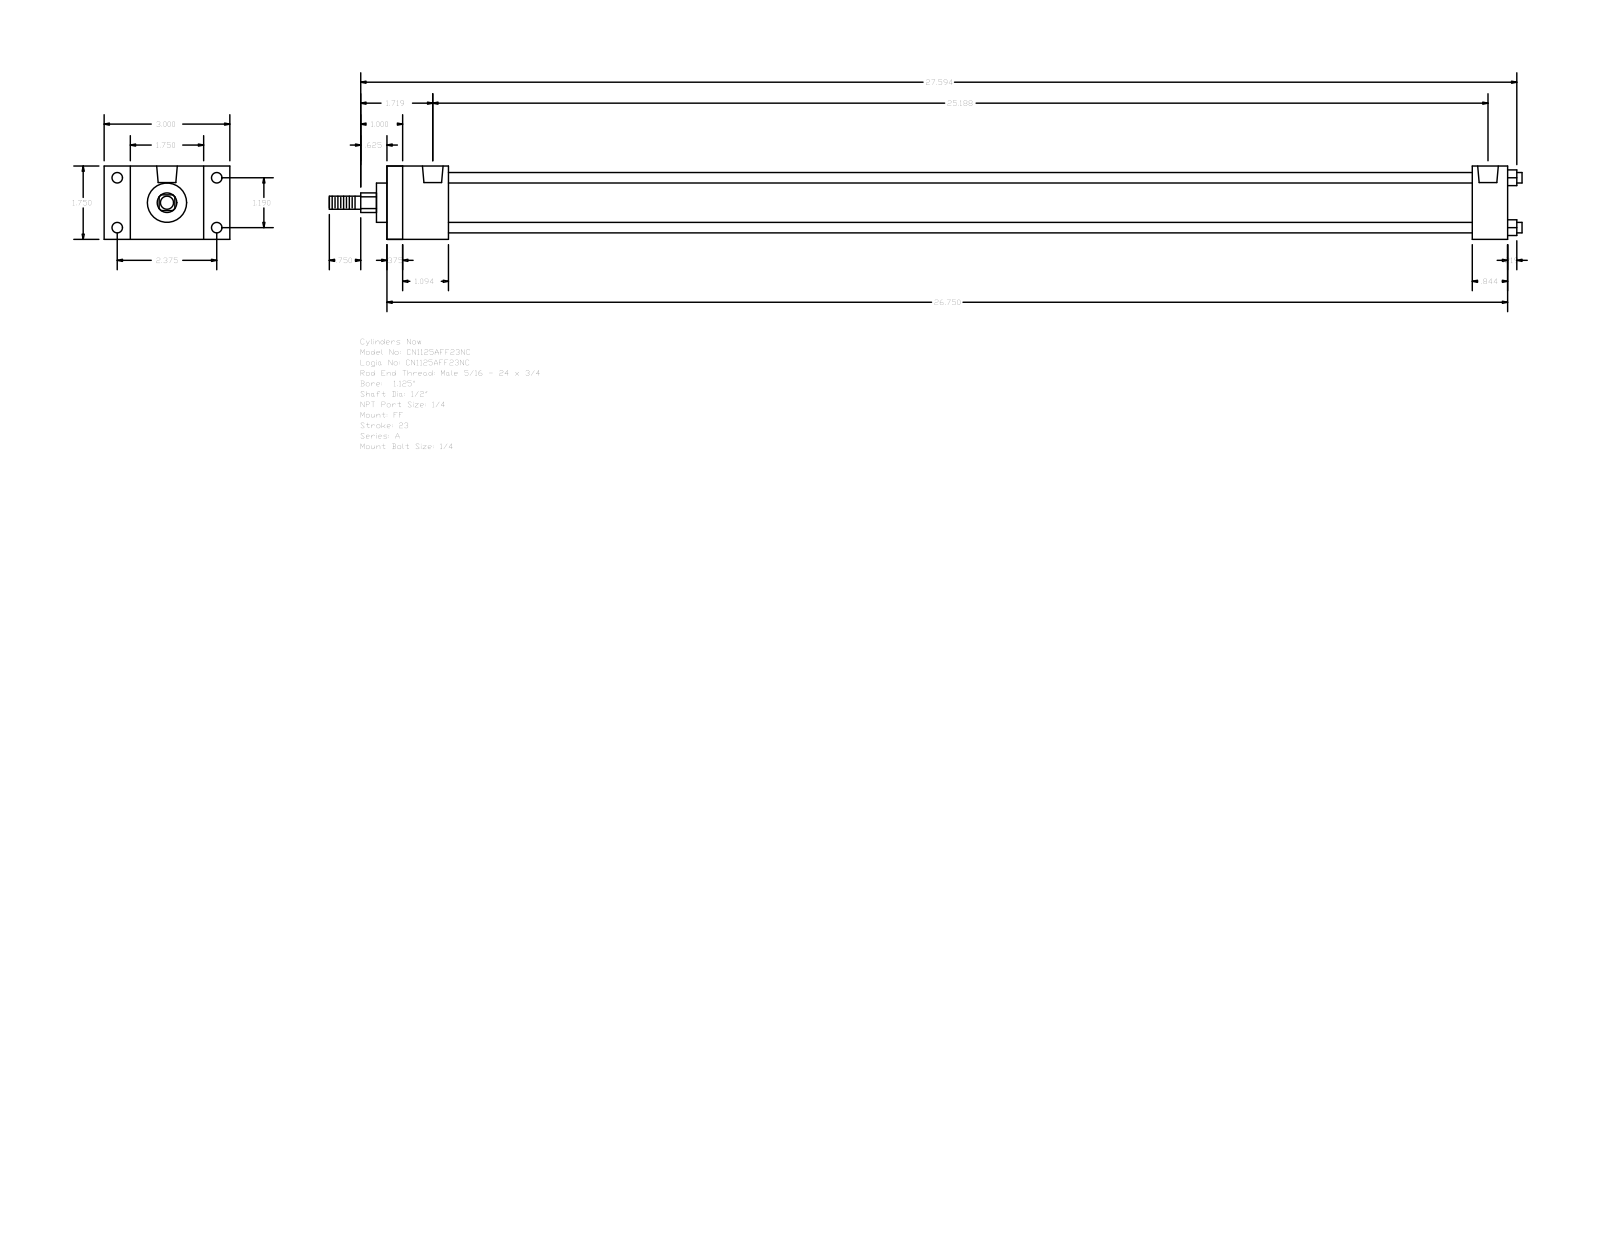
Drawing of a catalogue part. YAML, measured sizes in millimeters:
part_name: "A_FF__0112_0.5"
step_written_by: "GSSL Pune (CONFIG_CONTROL_DESIGN)"
units: millimeters
bodies: {solids: 0, faces: 92, planar: 64, cylindrical: 28, other: 0}
overall_size: [723.11, 76.2, 44.45]
round_holes:
  - {diameter: 5.56, count: 4}
  - {diameter: 6.35, count: 4}
  - {diameter: 12.49, count: 2}
round_bosses_or_shafts:
  - {diameter: 6.35, count: 4}
  - {diameter: 31.88, count: 1}
  - {diameter: 23.81, count: 1}
  - {diameter: 12.7, count: 1}
  - {diameter: 7.94, count: 1}
partial_cylinders:
  - {radius: 5.94, count: 1}
face_to_face_distances: [44.46, 679.45, 9.52, 669.93, 15.87, 658.01, 648.49, 21.44, 37.3, 27.78]
hole_center_spacings: [30.22, 60.32, 67.47, 636.59, 1.58, 1.59, 638.17, 638.18]
